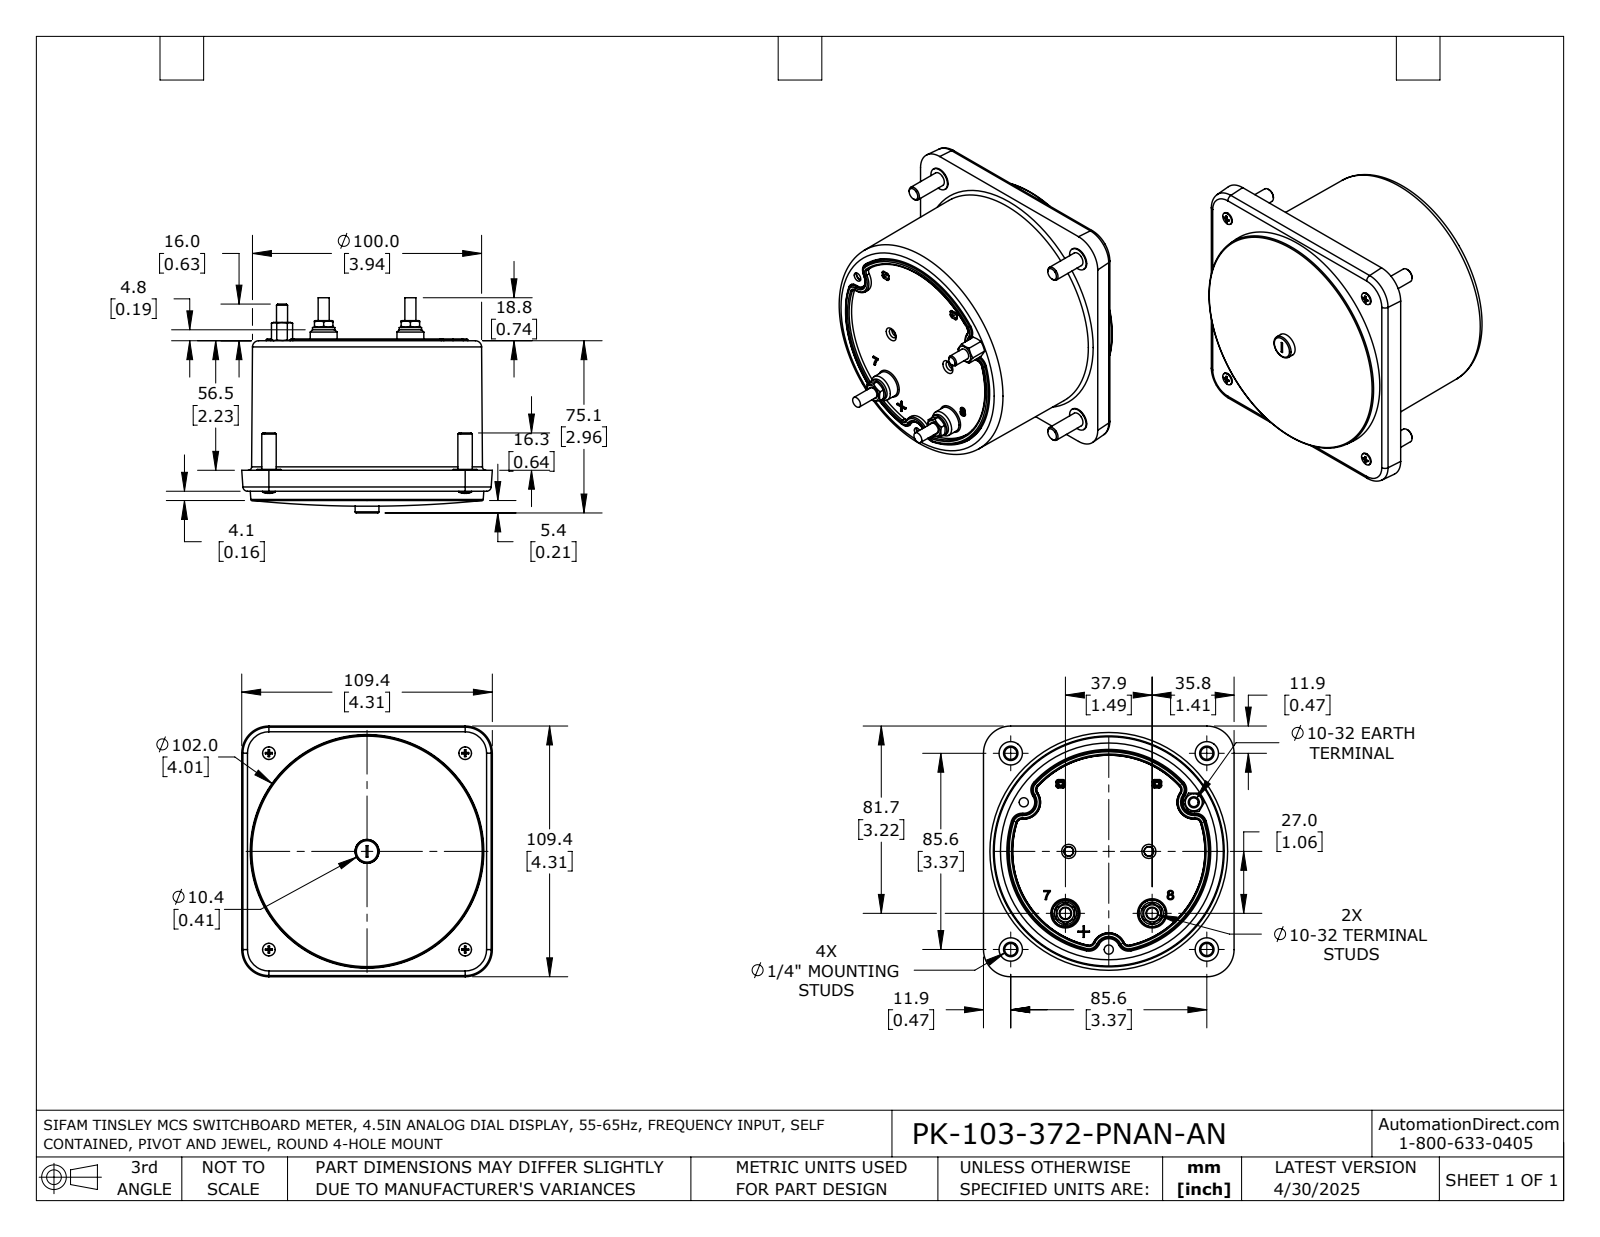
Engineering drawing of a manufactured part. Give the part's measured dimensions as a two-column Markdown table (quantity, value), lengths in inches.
| quantity | value |
| --- | --- |
| part name | PK-103-372-PNAN-AN |
| STEP written by | SolidWorks 2021 (AUTOMOTIVE_DESIGN) |
| units | inches |
| bodies | 1 solid, 609 faces (167 planar, 141 cylindrical, 301 other) |
| overall size | 4.307 × 4.307 × 3.697 |
| volume | 36.28 in³ |
| surface area | 82.21 in² |
| round holes (diameter × count) | 0.094 × 4, 0.138 × 4, 0.315 × 4, 0.157 × 3, 0.209 × 2 |
| round bosses / shafts (diameter × count) | 0.402 × 4, 0.248 × 4, 0.217 × 4, 0.114 × 4, 0.19 × 3, 0.384 × 2, 0.146 × 1 |
| partial cylindrical surfaces (radius × count) | 0.02 × 24, 0.189 × 9, 0.079 × 4, 1.752 × 1 |
| main face-to-face distances | 2.177, 2.537, 0.36, 0.048, 2.225, 2.585, 0.489, 2.715, 2.667, 0.129 |
| hole center spacings | 3.372, 3.37, 3.374, 3.378, 3.38, 4.769, 0.971, 1.126 |
